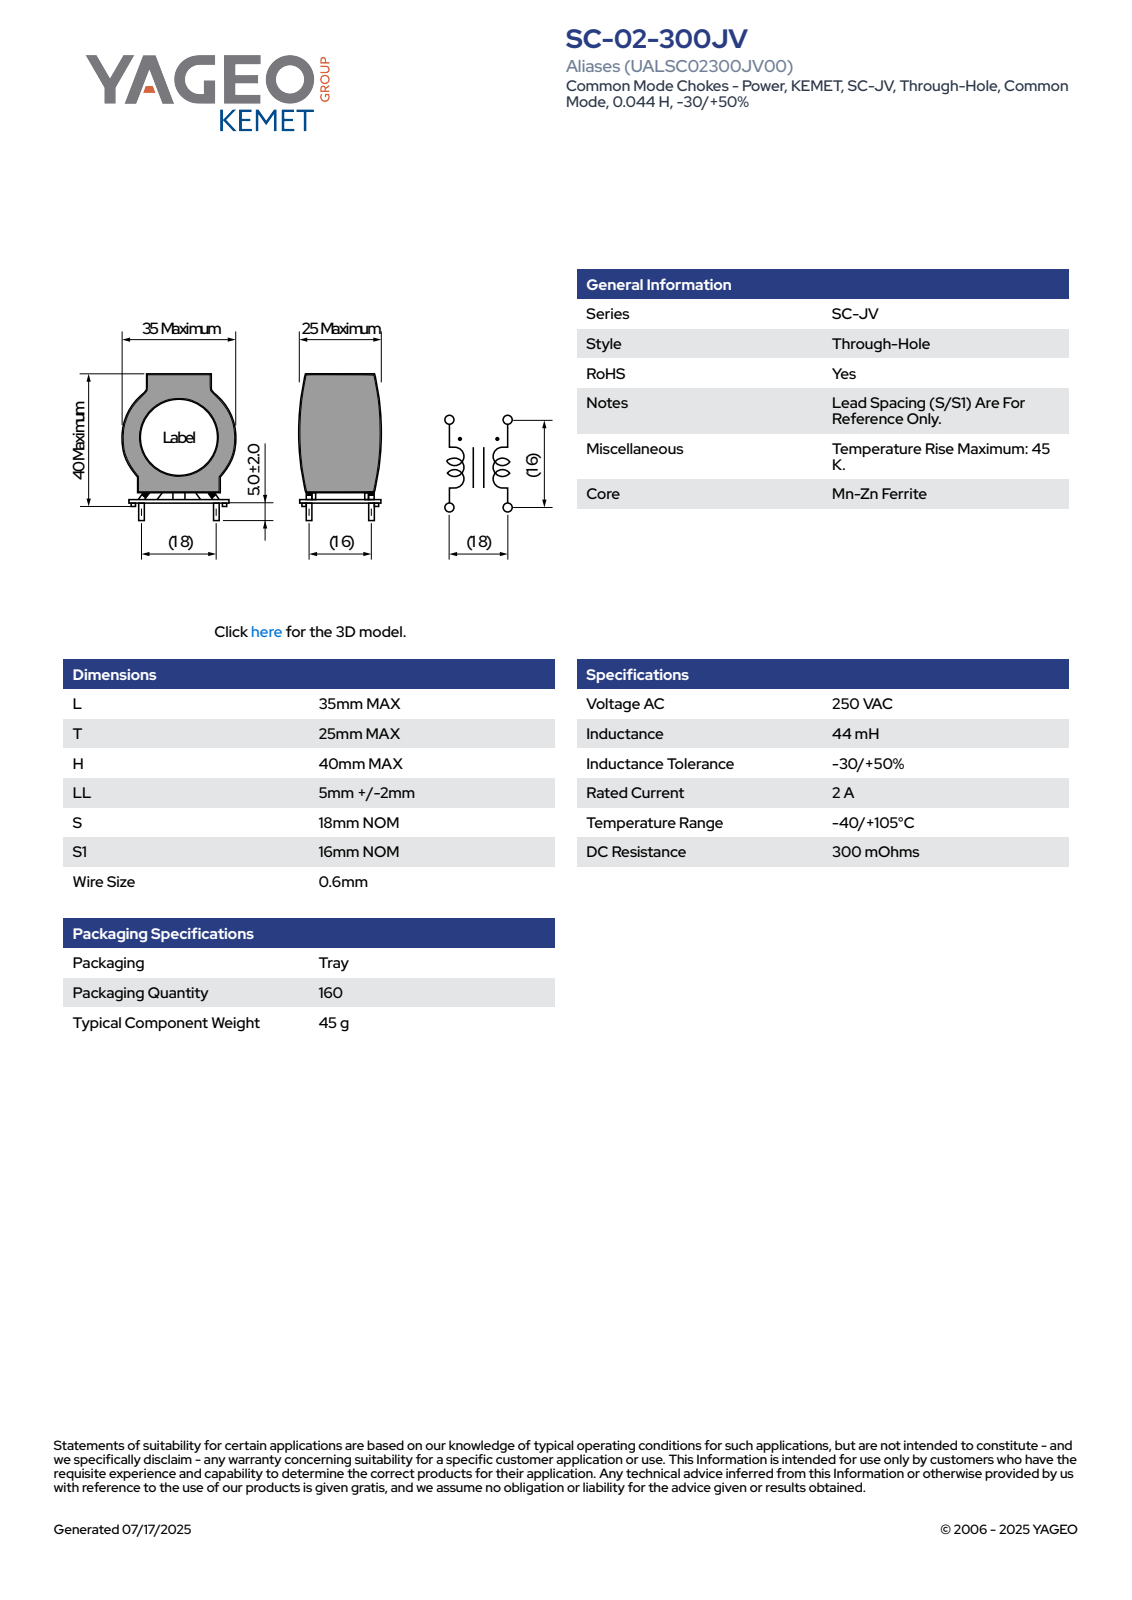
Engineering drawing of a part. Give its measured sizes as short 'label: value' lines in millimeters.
name: SC-02-300JV
written by: SolidWorks 2018 (AUTOMOTIVE_DESIGN)
unit: mm
bodies: 1 solid, 485 faces (186 planar, 157 cylindrical, 142 other)
size: 45.02 × 35 × 25
volume: 17 582 mm³; area: 13 171 mm²
holes: 4× ⌀1
bosses: 8× ⌀0.6, 4× ⌀1
rounds: 20× R0.5, 16× R0.3, 8× R1.5, 6× R1, 6× R2, 6× R5, 5× R4.5, 4× R0.7
face distances: 0.5, 24.5, 3, 2.5, 21.5, 22, 24, 25, 19, 2.4
hole spacings: 16, 18, 24.08
